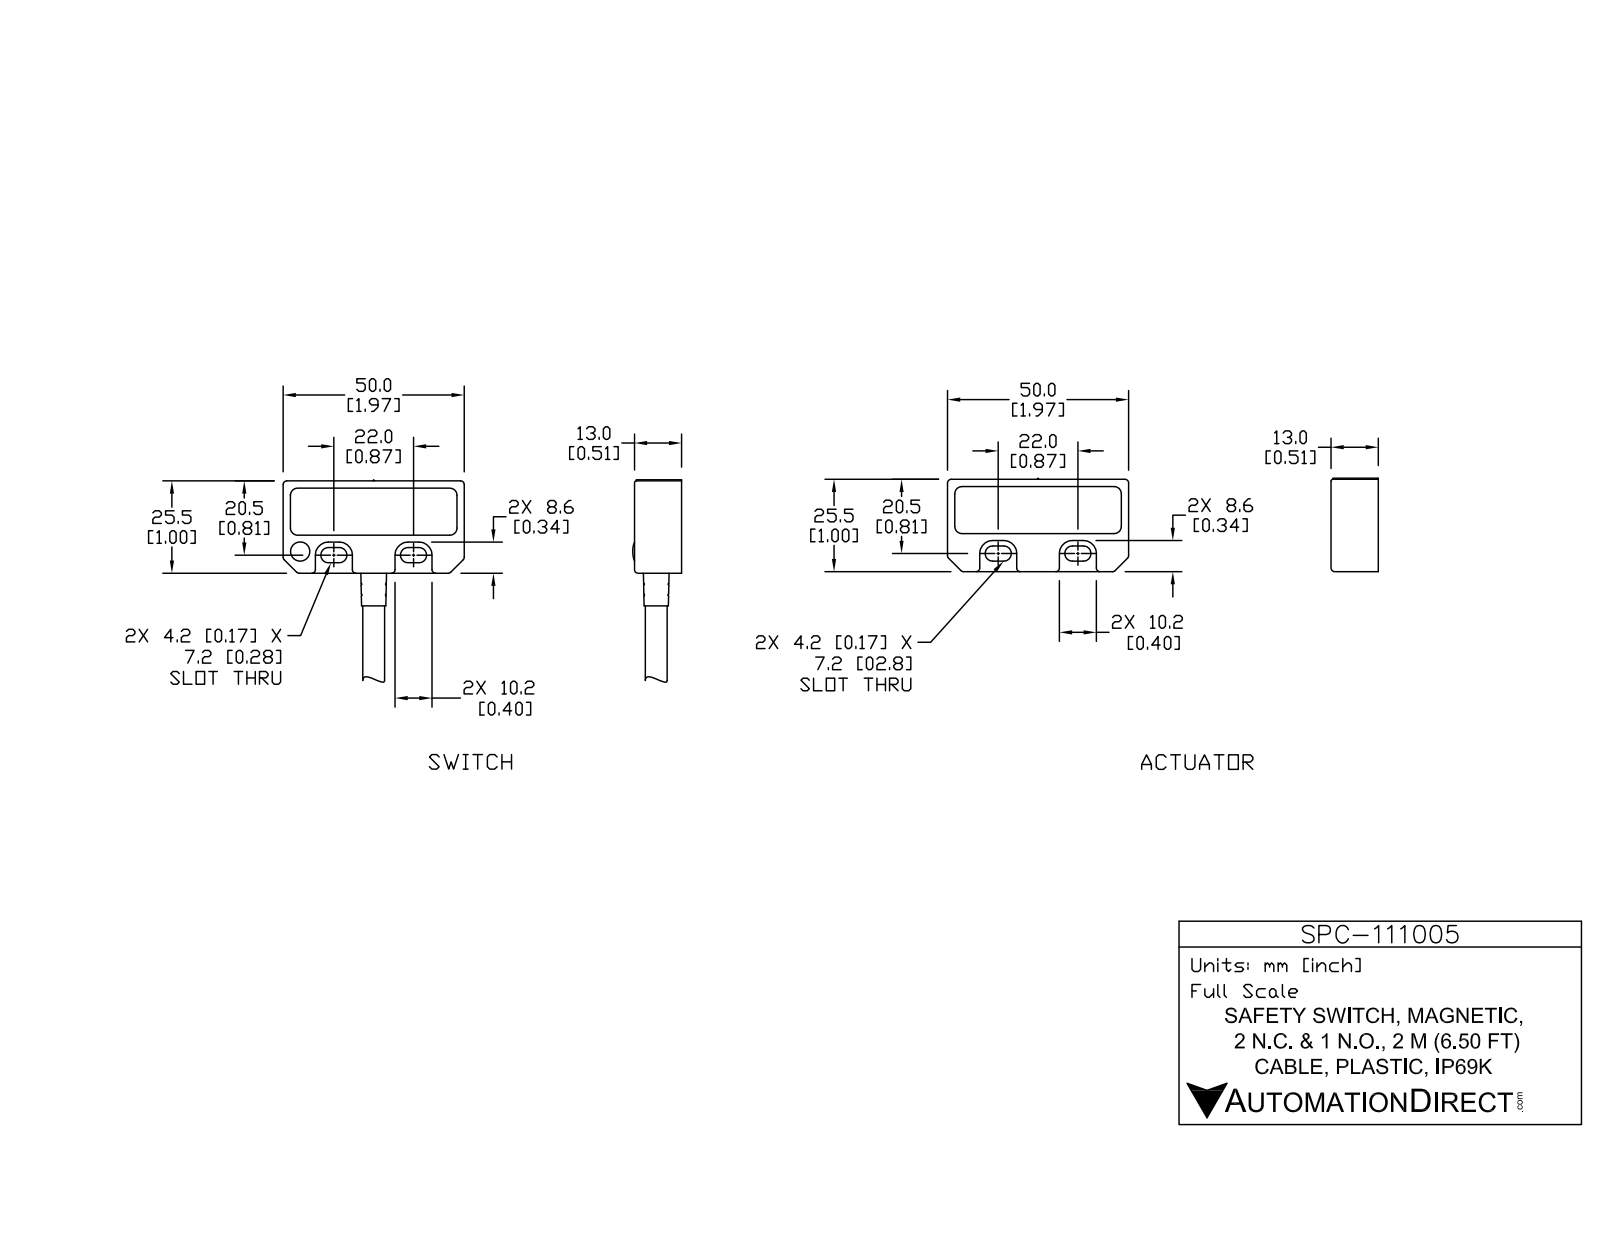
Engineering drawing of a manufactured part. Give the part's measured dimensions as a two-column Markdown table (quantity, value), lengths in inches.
| quantity | value |
| --- | --- |
| part name | SPC-111005_2; SPC-111005; SPC-111005_1 |
| STEP written by | SolidWorks 2017 (AUTOMOTIVE_DESIGN) |
| units | inches |
| bodies | 12 solids, 1147 faces (475 planar, 358 cylindrical, 314 other) |
| overall size | 8.091 × 1.969 × 0.543 |
| volume | 1.105 in³ |
| surface area | 36.31 in² |
| round holes (diameter × count) | 0.197 × 4, 0.119 × 1, 0.173 × 1, 0.213 × 1, 0.232 × 1, 0.276 × 1 |
| round bosses / shafts (diameter × count) | 0.079 × 4, 0.193 × 2, 0.031 × 2, 0.339 × 1, 0.299 × 1, 0.28 × 1, 0.236 × 1, 0.209 × 1 |
| partial cylindrical surfaces (radius × count) | 0.02 × 132, 0.039 × 36, 0.079 × 8, 0.083 × 8, 0.142 × 8, 0.181 × 8, 0.012 × 6, 0.14 × 4 |
| main face-to-face distances | 0.059, 0.457, 0.398, 0.047, 0.445, 0.504, 1.043, 0.098, 0.945, 1.909 |
| hole center spacings | 0.221, 0.862, 1.062, 1.065, 1.283, 1.492, 1.55, 1.559 |
